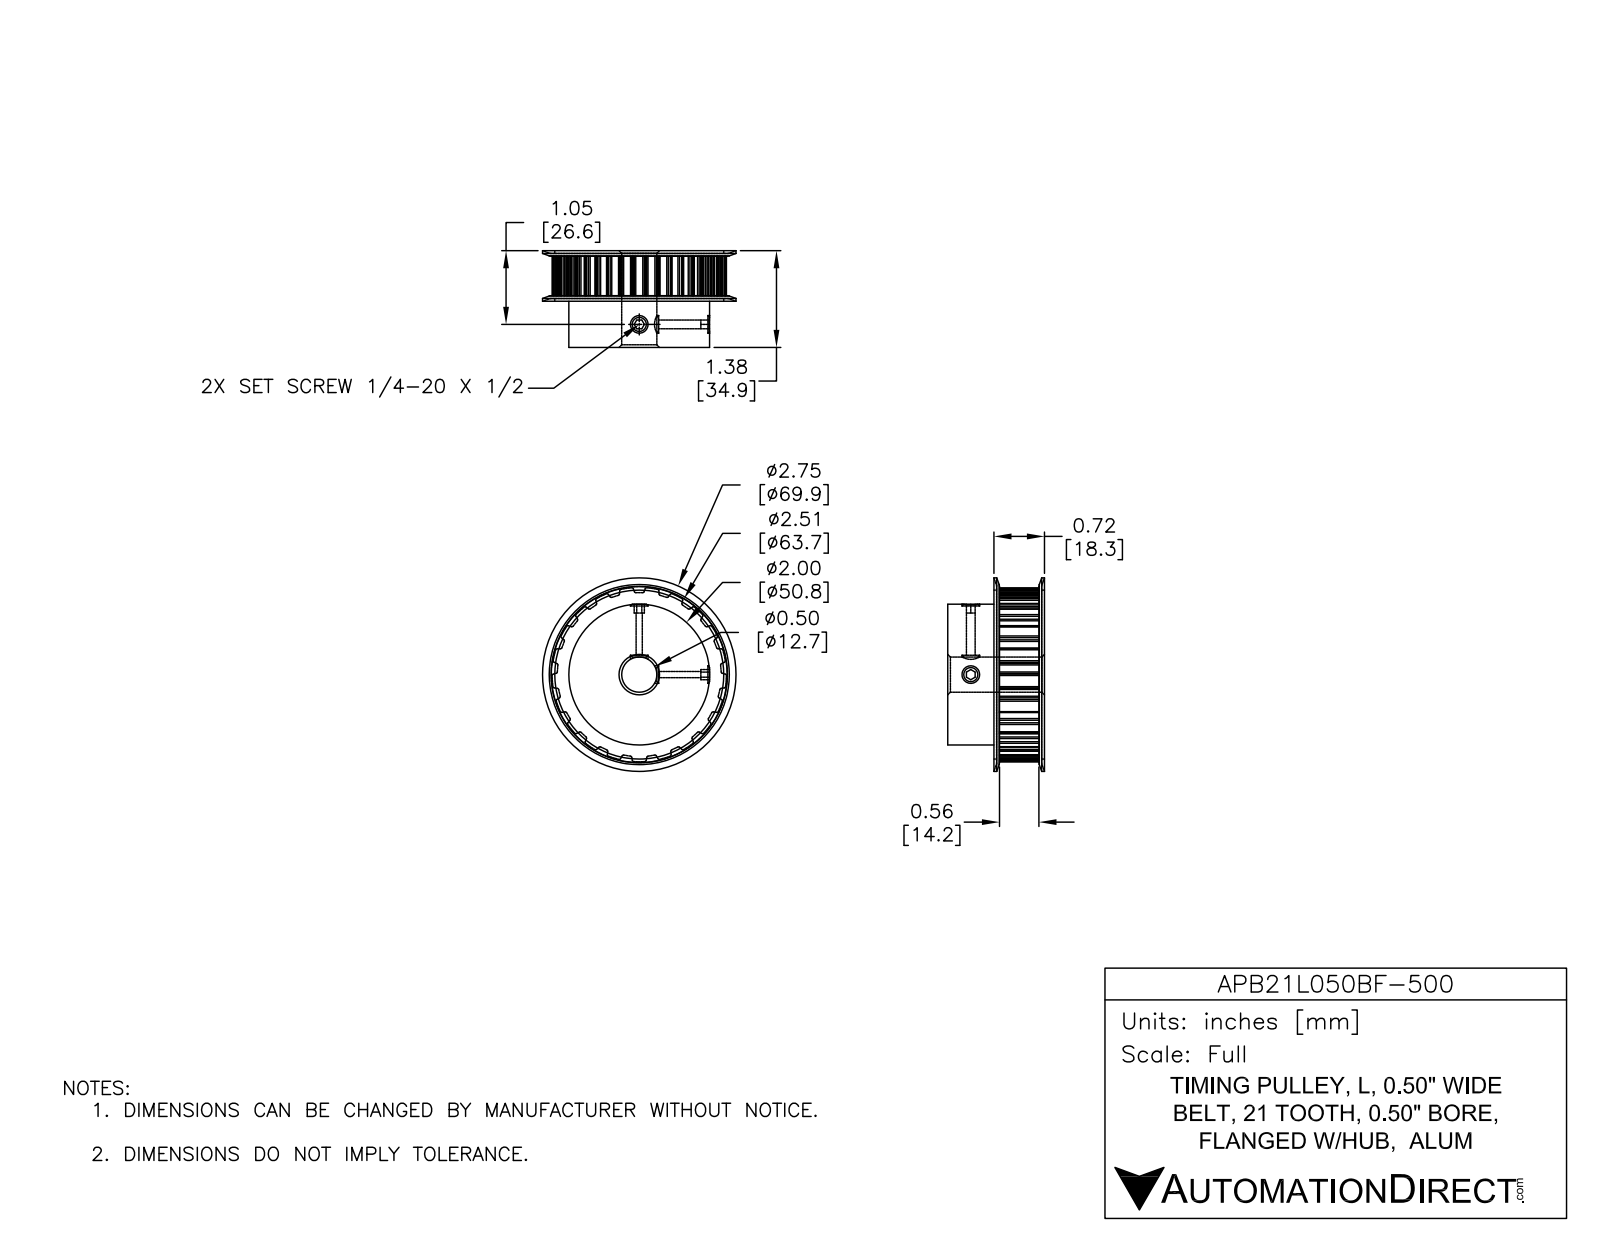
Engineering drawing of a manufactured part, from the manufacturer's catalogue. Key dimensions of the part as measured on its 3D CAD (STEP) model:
Part name (STEP PRODUCT): APB21L050BF-500
STEP written by: SolidWorks 2014 (AUTOMOTIVE_DESIGN)
Units: inches
Bodies: 1 solid, 172 faces (69 planar, 81 cylindrical, 22 other)
Overall size (bounding box): 2.75 × 2.75 × 1.313
Volume: 5.027 in³ · Surface area: 26.37 in²
Round holes (diameter × count): ⌀0.088 ×2, ⌀0.5 ×1
Round bosses / shafts (diameter × count): ⌀2 ×1
Partial cylindrical surfaces — rounded edges, fillets, slot ends (radius × count): R0.015 ×42, R1.184 ×1
Main face-to-face distances: 1.313, 0.71, 0.603, 0.04, 0.67, 1.273, 0.04, 0.63, 0.08, 1.233
